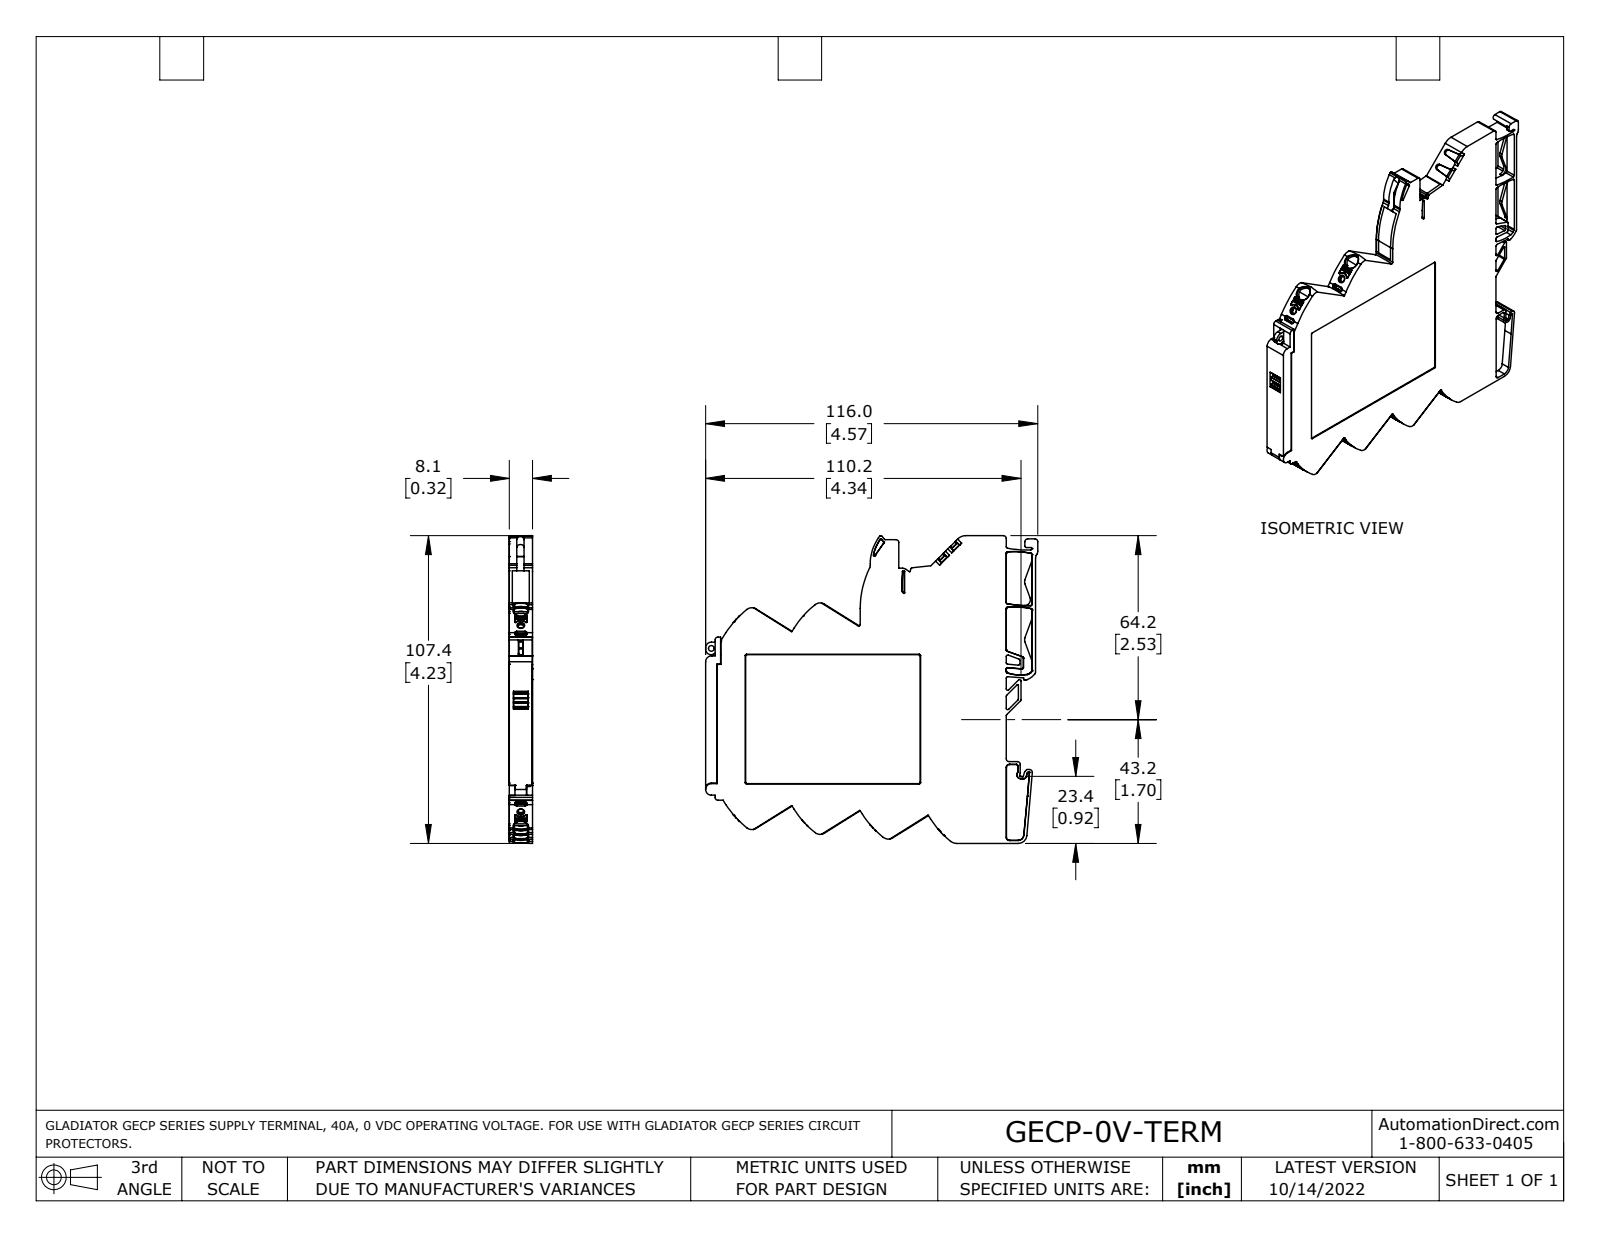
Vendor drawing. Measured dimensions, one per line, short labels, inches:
name: GECP-0V-TERM
written by: SolidWorks 2021 (AUTOMOTIVE_DESIGN)
unit: in
bodies: 1 solid, 1170 faces (546 planar, 466 cylindrical, 158 other)
size: 4.567 × 4.241 × 0.319
volume: 4.34 in³; area: 46.67 in²
holes: 6× ⌀0.083, 1× ⌀0.078, 1× ⌀0.087
bosses: 1× ⌀0.083
rounds: 58× R0.02, 45× R0.039, 43× R0.008, 28× R0.01, 27× R0.012, 13× R0.079, 12× R0.009, 12× R1.299
face distances: 0.319, 0.311, 0.309, 0.317, 0.201, 0.157, 0.118, 0.354, 3.935, 4.093
hole spacings: 0.559, 1.118, 0.559, 1.677, 1.937
